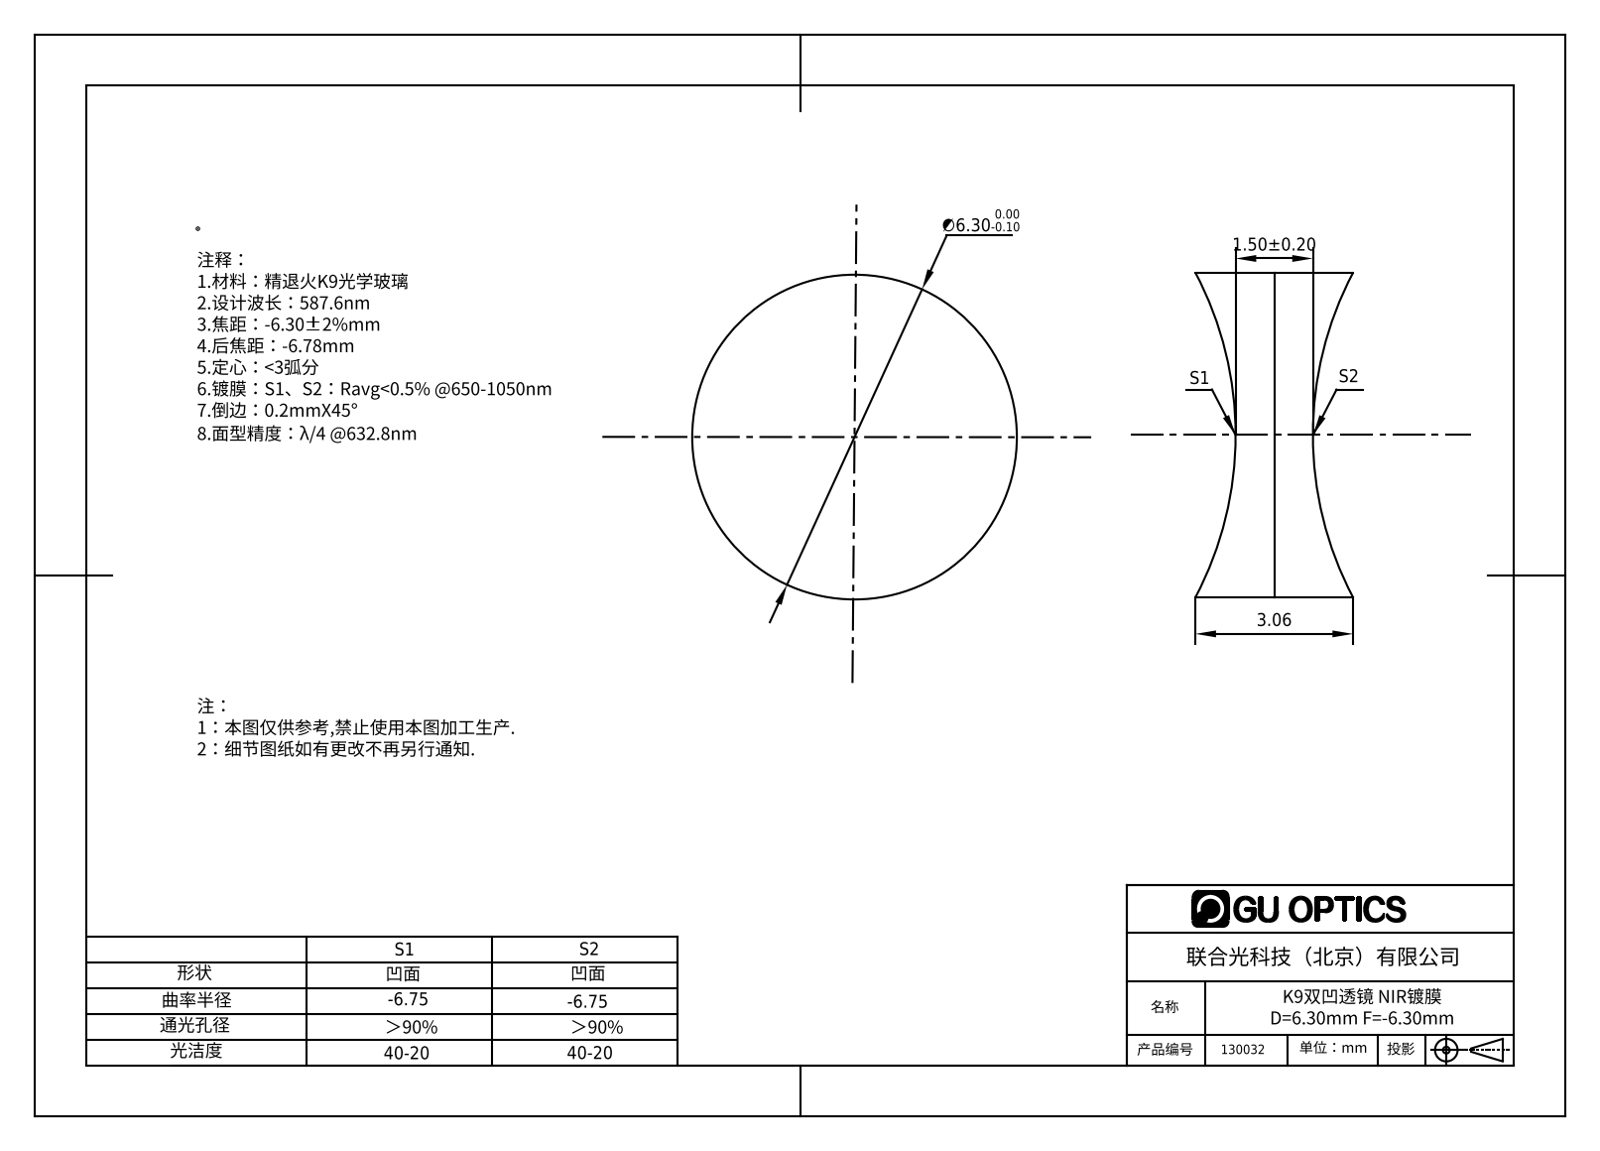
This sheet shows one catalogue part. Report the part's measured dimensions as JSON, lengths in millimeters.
{"part_name": "130006", "step_written_by": "SolidWorks 2016 (AUTOMOTIVE_DESIGN)", "units": "millimeters", "bodies": {"solids": 1, "faces": 6, "planar": 0, "cylindrical": 2, "other": 4}, "overall_size": [6.3, 6.3, 3.06], "volume_mm3": 71, "surface_area_mm2": 127, "round_bosses_or_shafts": [[6.3, 1]]}
